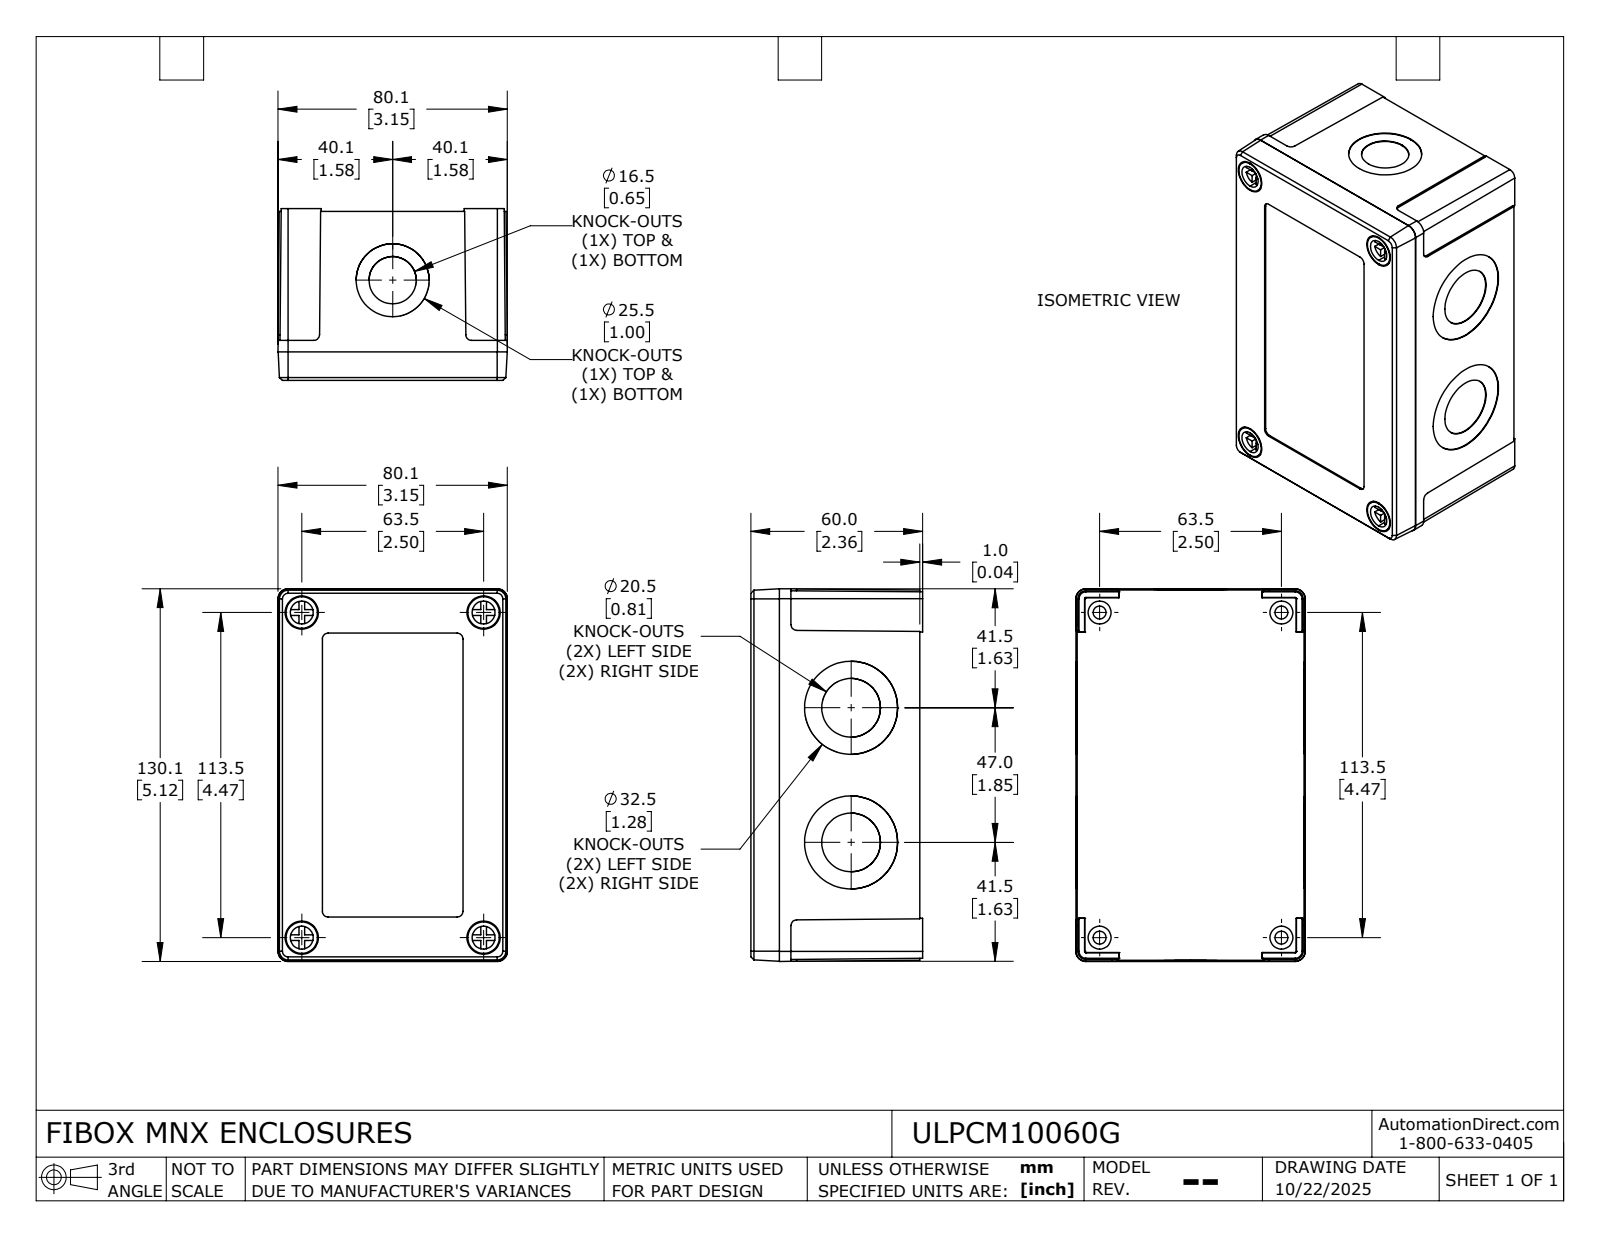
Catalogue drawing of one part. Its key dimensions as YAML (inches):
part_name: "ULPCM10060G_Default"
step_written_by: "SolidWorks 2024 (CONFIG_CONTROL_DESIGN)"
units: inches
bodies: {solids: 6, faces: 510, planar: 294, cylindrical: 176, other: 40}
overall_size: [5.122, 3.154, 2.362]
volume: 9.961
surface_area: 153.5
round_holes:
  - {diameter: 0.126, count: 8}
  - {diameter: 0.157, count: 8}
  - {diameter: 0.177, count: 4}
  - {diameter: 0.315, count: 4}
  - {diameter: 0.457, count: 4}
  - {diameter: 0.807, count: 4}
  - {diameter: 1.28, count: 4}
  - {diameter: 0.65, count: 2}
  - {diameter: 1.004, count: 2}
round_bosses_or_shafts:
  - {diameter: 0.315, count: 8}
  - {diameter: 0.098, count: 8}
  - {diameter: 0.433, count: 4}
  - {diameter: 0.283, count: 4}
partial_cylinders:
  - {radius: 0.079, count: 8}
  - {radius: 0.056, count: 6}
  - {radius: 0.021, count: 4}
  - {radius: 0.197, count: 4}
  - {radius: 0.023, count: 2}
face_to_face_distances: [0.165, 2.232, 0.118, 2.114, 2.303, 2.185, 0.071, 2.205, 1.929, 2.323]
hole_center_spacings: [0.841, 0.888, 1.333, 1.476, 1.939, 2.159, 2.174, 2.281]
